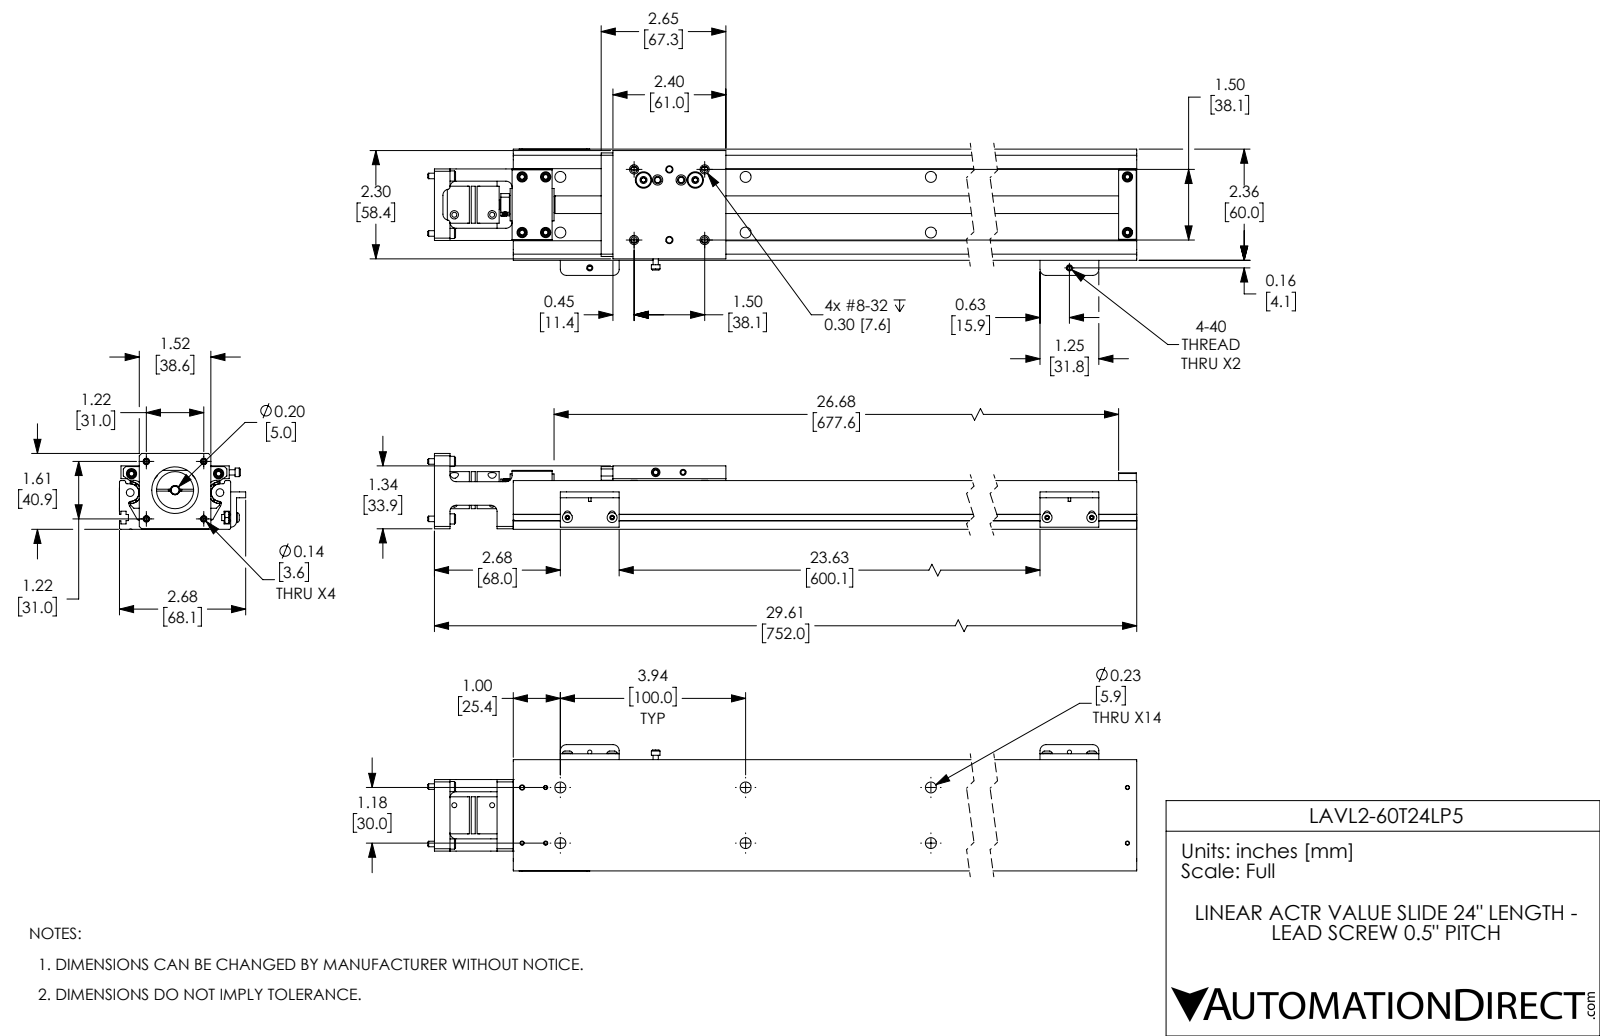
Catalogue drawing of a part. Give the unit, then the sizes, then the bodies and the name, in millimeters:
Units: millimetres
Overall size (bounding box): 755.6 × 68.1 × 40.9
Round holes (diameter × count): ⌀2.3 ×18, ⌀5.9 ×14, ⌀3.6 ×10, ⌀5.6 ×10, ⌀3.5 ×6, ⌀3.6 ×4, ⌀0.8 ×2, ⌀2.5 ×2, ⌀2.7 ×2, ⌀3.2 ×2, ⌀4 ×2, ⌀4.2 ×2
Round bosses / shafts (diameter × count): ⌀2.8 ×15, ⌀4.6 ×11, ⌀5.5 ×4, ⌀5.4 ×4, ⌀3 ×4, ⌀7.9 ×2, ⌀4.8 ×2, ⌀4.2 ×2
Partial cylindrical surfaces — rounded edges, fillets, slot ends (radius × count): R3.3 ×20, R0.8 ×12, R1.8 ×8, R1.5 ×4, R0.5 ×3, R1 ×2, R1.3 ×2, R1.7 ×2
Main face-to-face distances: 5.1, 60, 3.6, 2.9, 4.7, 56.4, 2.8, 0.8, 59.2, 55.7
Hole centre spacings: 100, 104.4, 30, 200, 202.2, 300, 301.5, 400
Volume: 553 100 mm³ · Surface area: 285 400 mm²
Bodies: 52 solids, 2140 faces (1295 planar, 537 cylindrical, 308 other)
Part name (STEP PRODUCT): LAVL2-60T24LP5; LAVL2-60T24LP5_BLOCK; LAVL2-60T24LP5_BODY
STEP written by: SolidWorks 2017 (AUTOMOTIVE_DESIGN)
